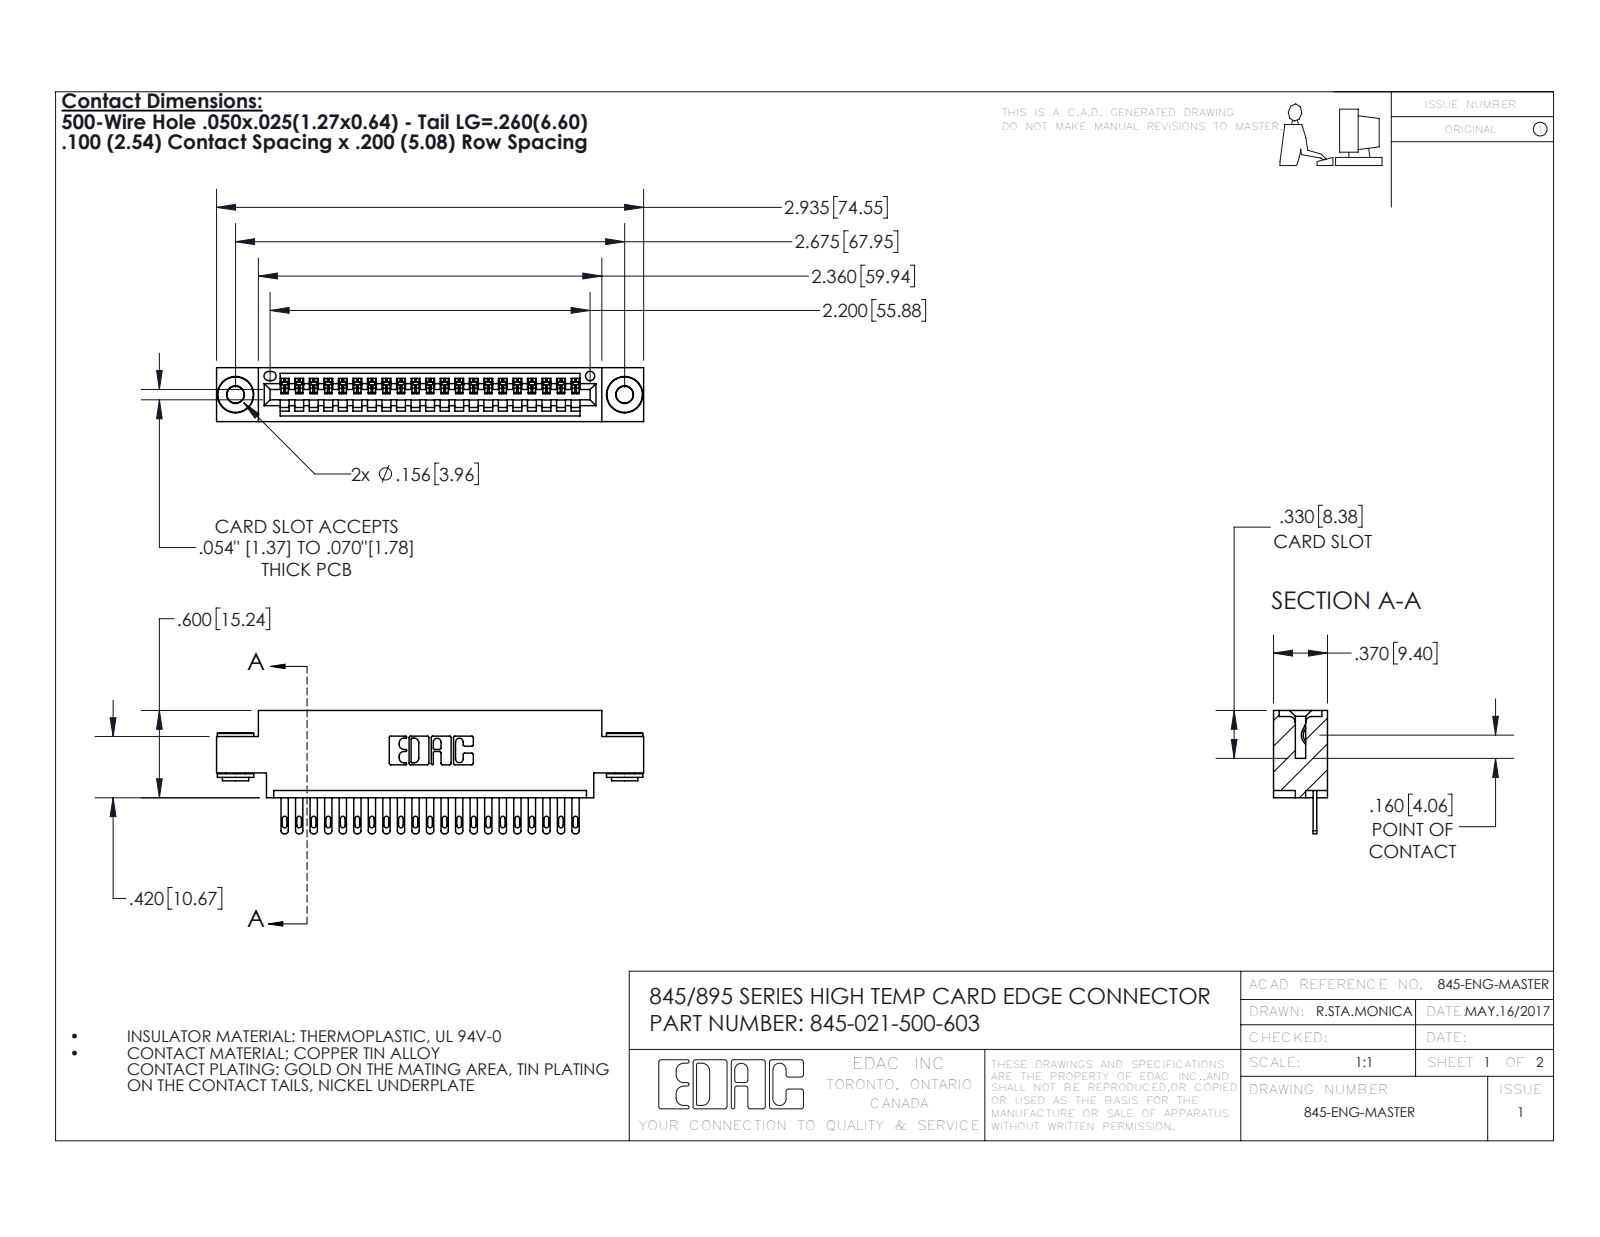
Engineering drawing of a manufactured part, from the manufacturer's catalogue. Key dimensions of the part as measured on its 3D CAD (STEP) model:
Part name (STEP PRODUCT): 345 Part_0.170 Offset - 0.156 Dia-TH; 345-021-500-603; 345-250-002_345-250-002-102; 345-292-001_345-293-100
STEP written by: SolidWorks 2016 (CONFIG_CONTROL_DESIGN)
Units: inches
Bodies: 24 solids, 1302 faces (808 planar, 486 cylindrical, 8 other)
Overall size (bounding box): 2.935 × 0.847 × 0.37
Volume: 0.417 in³ · Surface area: 14.22 in²
Round holes (diameter × count): ⌀0.116 ×2, ⌀0.156 ×2, ⌀0.064 ×1
Round bosses / shafts (diameter × count): ⌀0.25 ×2, ⌀0.18 ×2, ⌀0.136 ×2
Partial cylindrical surfaces — rounded edges, fillets, slot ends (radius × count): R0.006 ×42, R0.016 ×42, R0.02 ×42, R0.01 ×22, R0.007 ×6, R0.031 ×6, R0.026 ×3, R0.031 ×2
Main face-to-face distances: 0.072, 0.298, 0.37, 0.2, 0.098, 0.272, 0.025, 0.225, 0.175, 0.1
Hole centre spacings: 0.27, 2.441, 2.675
